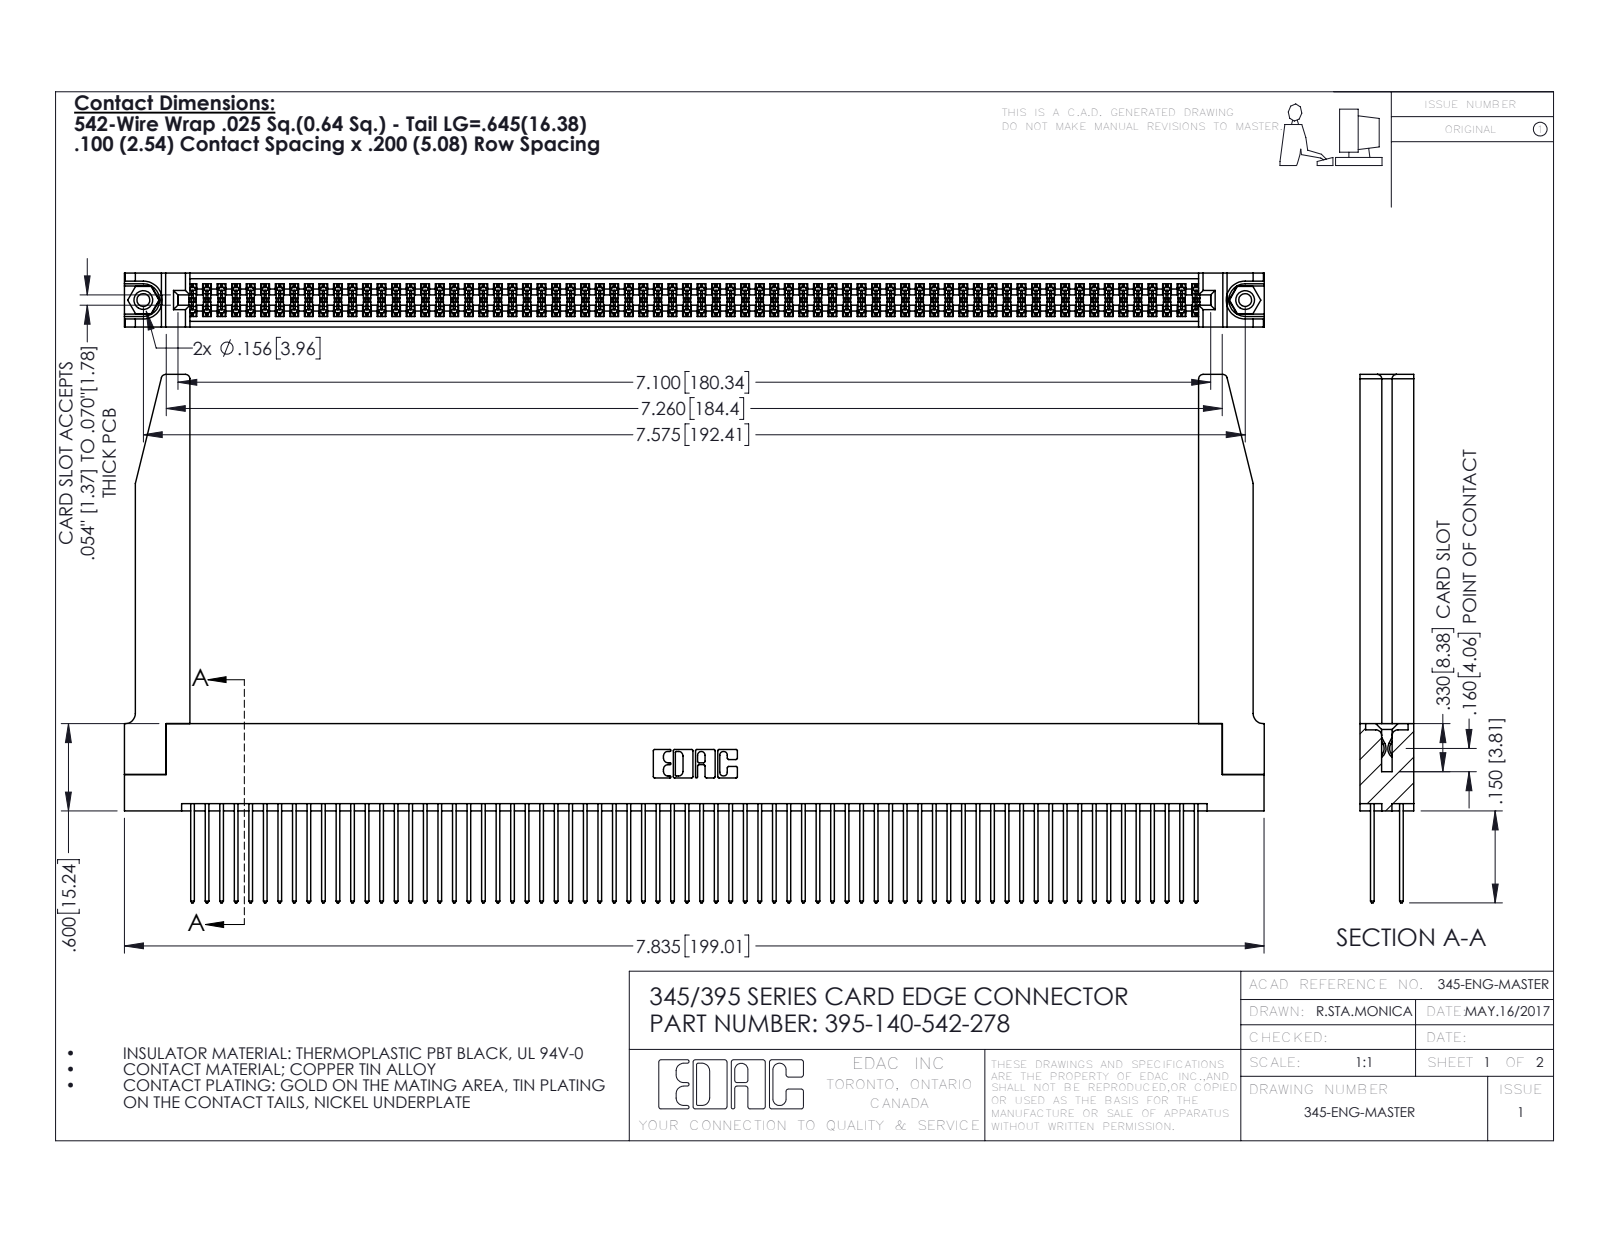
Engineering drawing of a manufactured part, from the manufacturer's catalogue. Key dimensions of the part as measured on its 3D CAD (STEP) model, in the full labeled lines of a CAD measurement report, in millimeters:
Part name (STEP PRODUCT): 345-220-078_345-220-078; 345 Part_Flush Mounting Lugs - 0.156 Dia-TH; 345-292-001_345-293-142; 395-140-542-278 (+1 more)
STEP written by: SolidWorks 2016 (CONFIG_CONTROL_DESIGN)
Units: millimetres
Bodies: 145 solids, 7360 faces (4842 planar, 2466 cylindrical, 52 other)
Overall size (bounding box): 199 × 92.3 × 9.4
Volume: 28 020 mm³ · Surface area: 40 360 mm²
Round holes (diameter × count): ⌀2.3 ×2, ⌀3.2 ×2, ⌀4 ×2, ⌀1.6 ×1
Round bosses / shafts (diameter × count): ⌀3.9 ×2
Partial cylindrical surfaces — rounded edges, fillets, slot ends (radius × count): R0.2 ×210, R0.3 ×140, R0.3 ×22, R0.8 ×8, R0.2 ×6, R0.8 ×6, R0.7 ×3, R0.4 ×2
Main face-to-face distances: 1.8, 7.6, 5.1, 9.4, 2.5, 6.9, 0.6, 5.7, 4.4, 3.8
Hole centre spacings: 6.9, 186.4, 192.4
